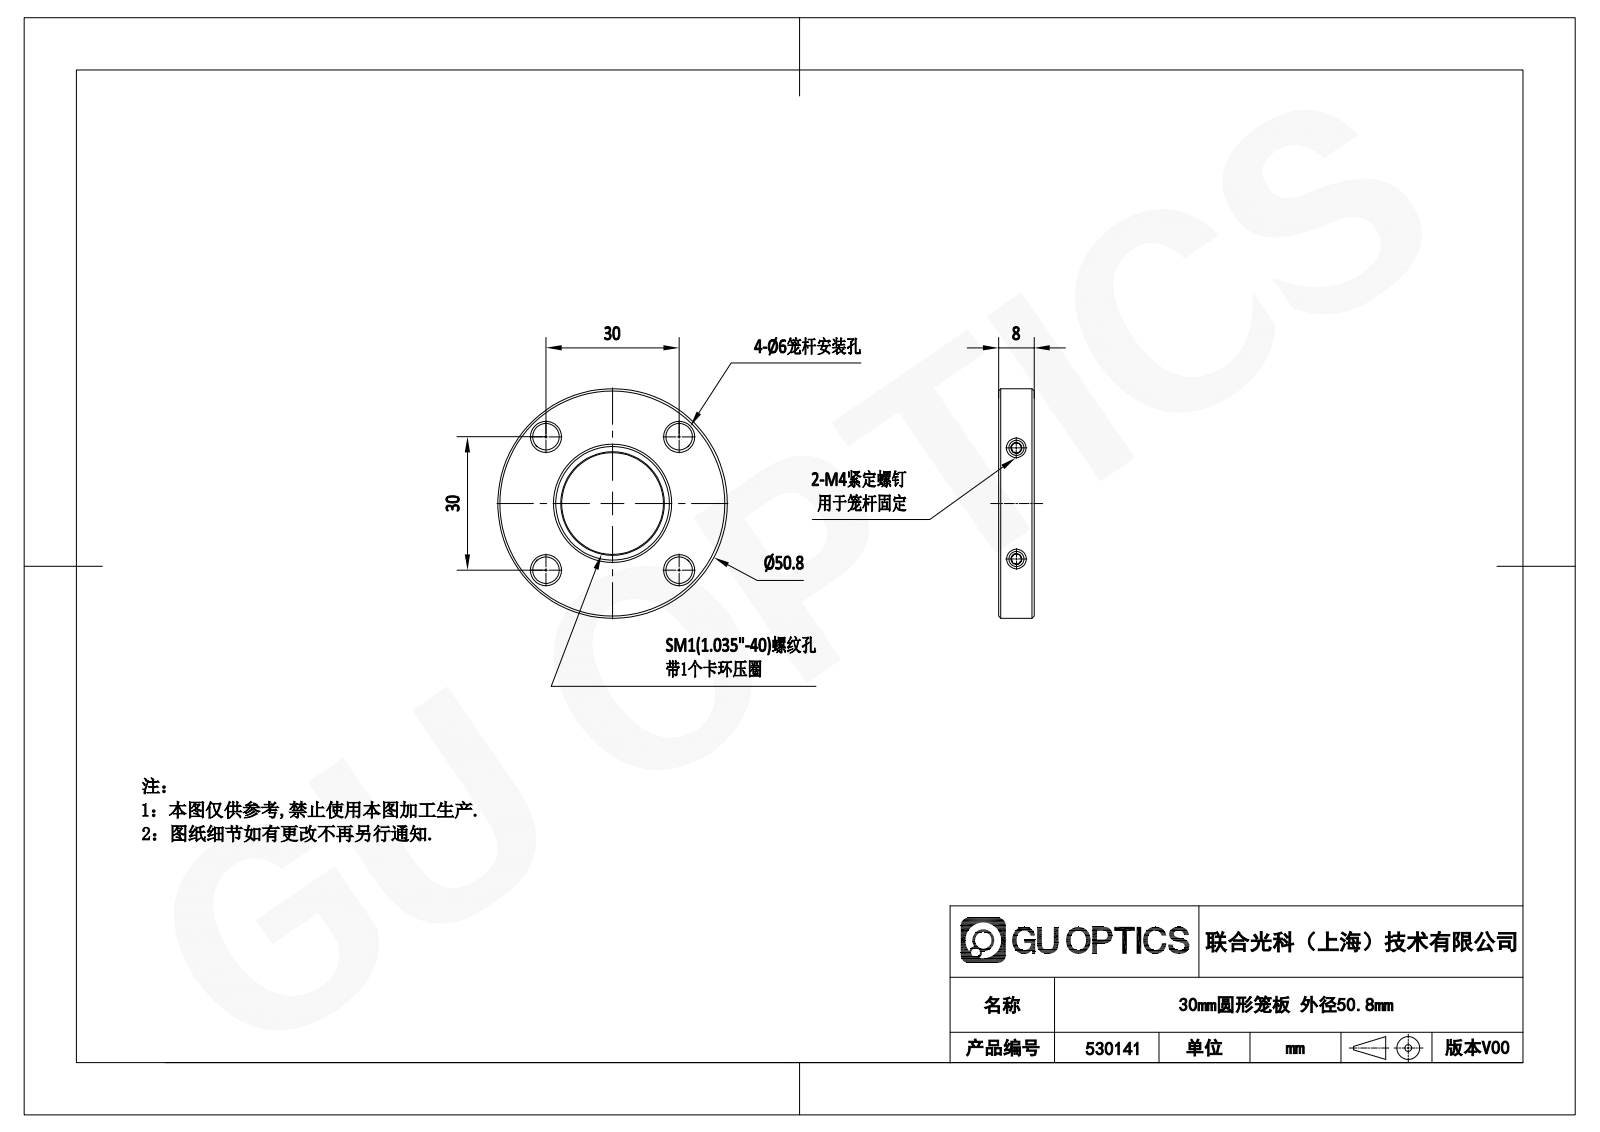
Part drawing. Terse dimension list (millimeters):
name: 530141
written by: SolidWorks 2020 (CONFIG_CONTROL_DESIGN)
unit: mm
bodies: 6 solids, 125 faces (51 planar, 20 cylindrical, 54 other)
size: 50.8 × 50.8 × 8
volume: 11 211 mm³; area: 6 124 mm²
holes: 4× ⌀6, 2× ⌀3.3, 2× ⌀4.5, 1× ⌀22.9, 1× ⌀25.65
bosses: 2× ⌀4, 1× ⌀50.8, 1× ⌀26.29
face distances: 8, 2, 6, 2.1, 0.58, 41.38, 39.96, 1.42, 39.38, 40.8
hole spacings: 21.21, 30, 42.43, 25
